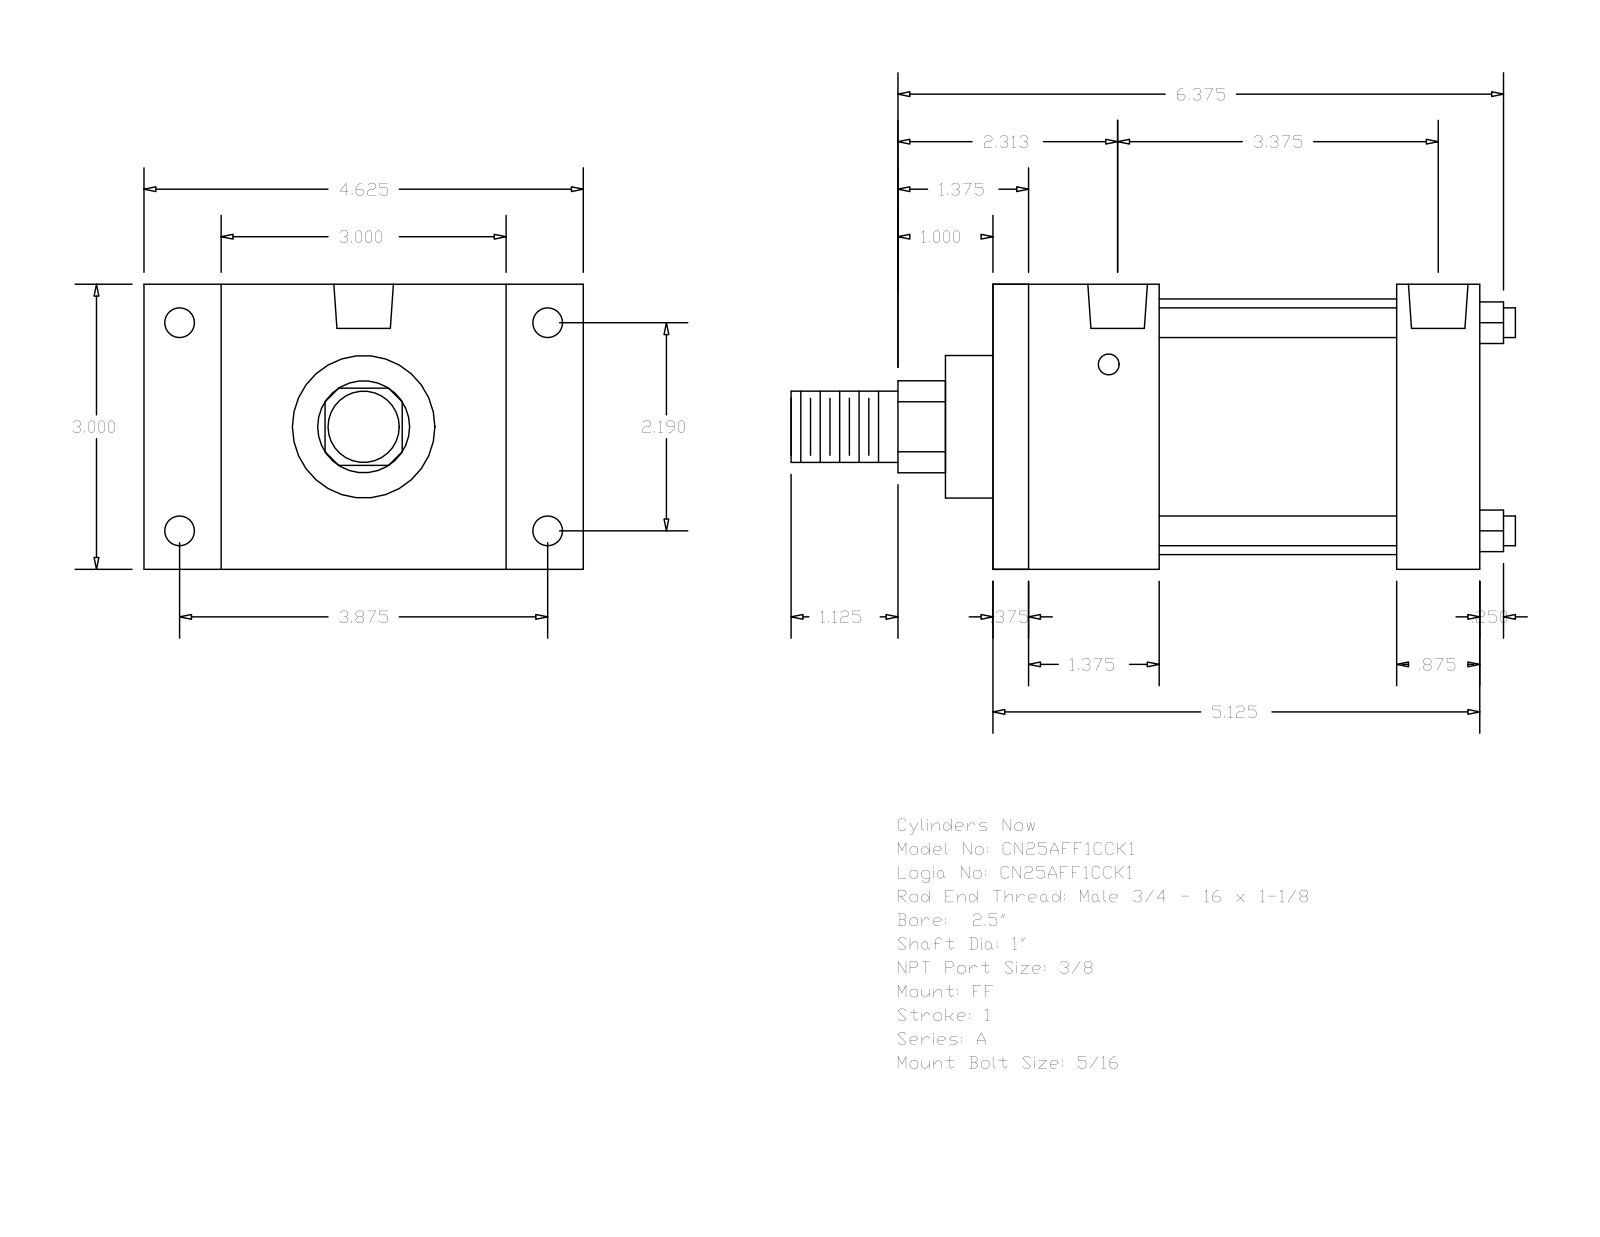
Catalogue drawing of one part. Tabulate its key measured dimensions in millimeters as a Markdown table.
| quantity | value |
| --- | --- |
| part name | A_FF__0250_1 |
| STEP written by | GSSL Pune (CONFIG_CONTROL_DESIGN) |
| units | millimeters |
| bodies | 0 solids, 92 faces (64 planar, 28 cylindrical, 0 other) |
| overall size | 193.68 × 117.47 × 76.2 |
| round holes (diameter × count) | 5.56 × 4, 7.94 × 4, 15.93 × 2 |
| round bosses / shafts (diameter × count) | 7.94 × 4, 68.33 × 1, 38.1 × 1, 25.4 × 1, 19.05 × 1 |
| partial cylindrical surfaces (radius × count) | 12.29 × 1 |
| main face-to-face distances | 76.2, 130.17, 120.65, 9.52, 22.22, 44.45, 107.95, 34.93, 98.43, 63.5 |
| hole center spacings | 2.38, 55.62, 88.1, 90.48, 98.42, 113.05, 85.72 |
